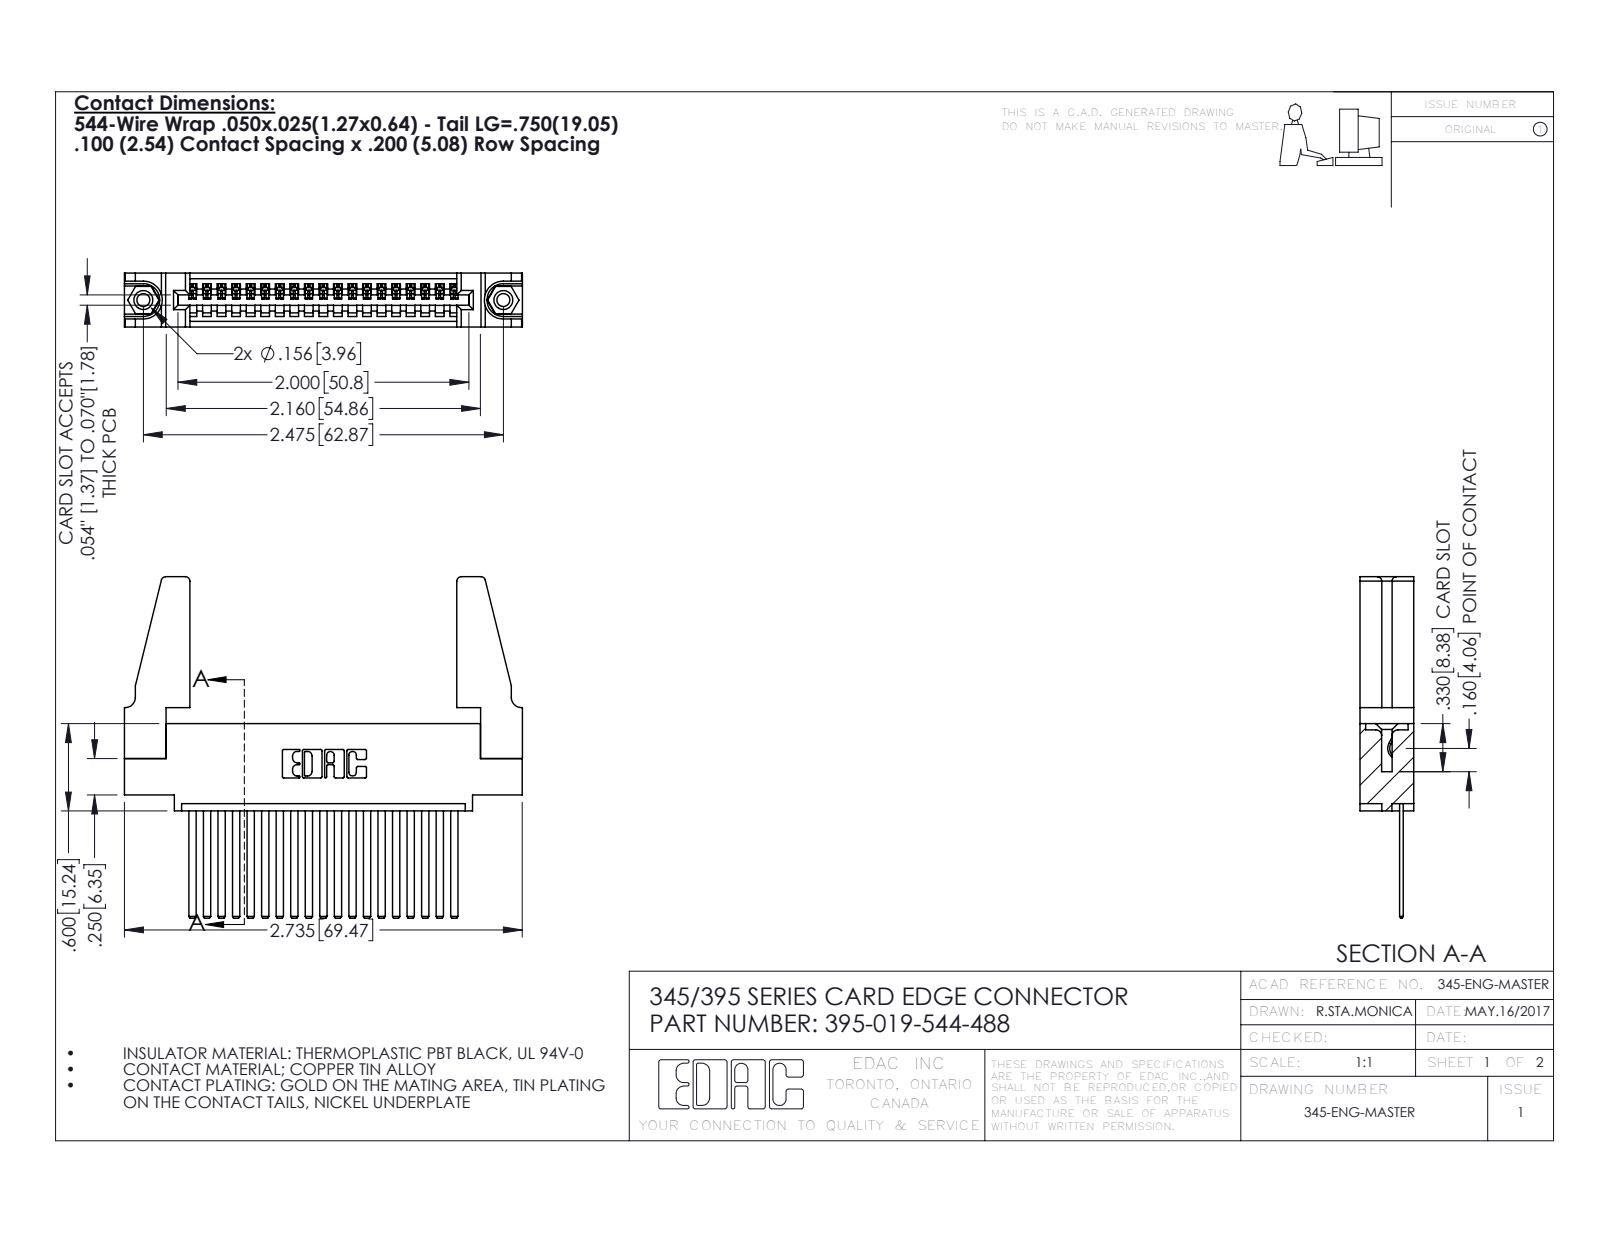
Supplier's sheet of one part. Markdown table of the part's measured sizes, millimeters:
| quantity | value |
| --- | --- |
| part name | 395-019-544-488; 345-250-001_345-250-001-102; 345 Part_0.110 Offset - 0.156 Dia-TH; 345-292-001_345-293-144 (+1 more) |
| STEP written by | SolidWorks 2016 (CONFIG_CONTROL_DESIGN) |
| units | millimeters |
| bodies | 24 solids, 1242 faces (840 planar, 386 cylindrical, 16 other) |
| overall size | 69.5 × 59.6 × 9.4 |
| volume | 9 820 mm³ |
| surface area | 12 280 mm² |
| round holes (diameter × count) | 2.3 × 2, 3.2 × 2, 4 × 2, 1.6 × 1 |
| round bosses / shafts (diameter × count) | 3.9 × 2 |
| partial cylindrical surfaces (radius × count) | 0.2 × 38, 0.3 × 22, 0.8 × 8, 0.2 × 6, 0.8 × 6, 0.7 × 3, 0.8 × 2, 1 × 2 |
| main face-to-face distances | 1.8, 7.6, 9.4, 2.5, 6.9, 0.6, 5.1, 5.7, 3.8, 3.8 |
| hole center spacings | 6.9, 56.9, 62.9 |
